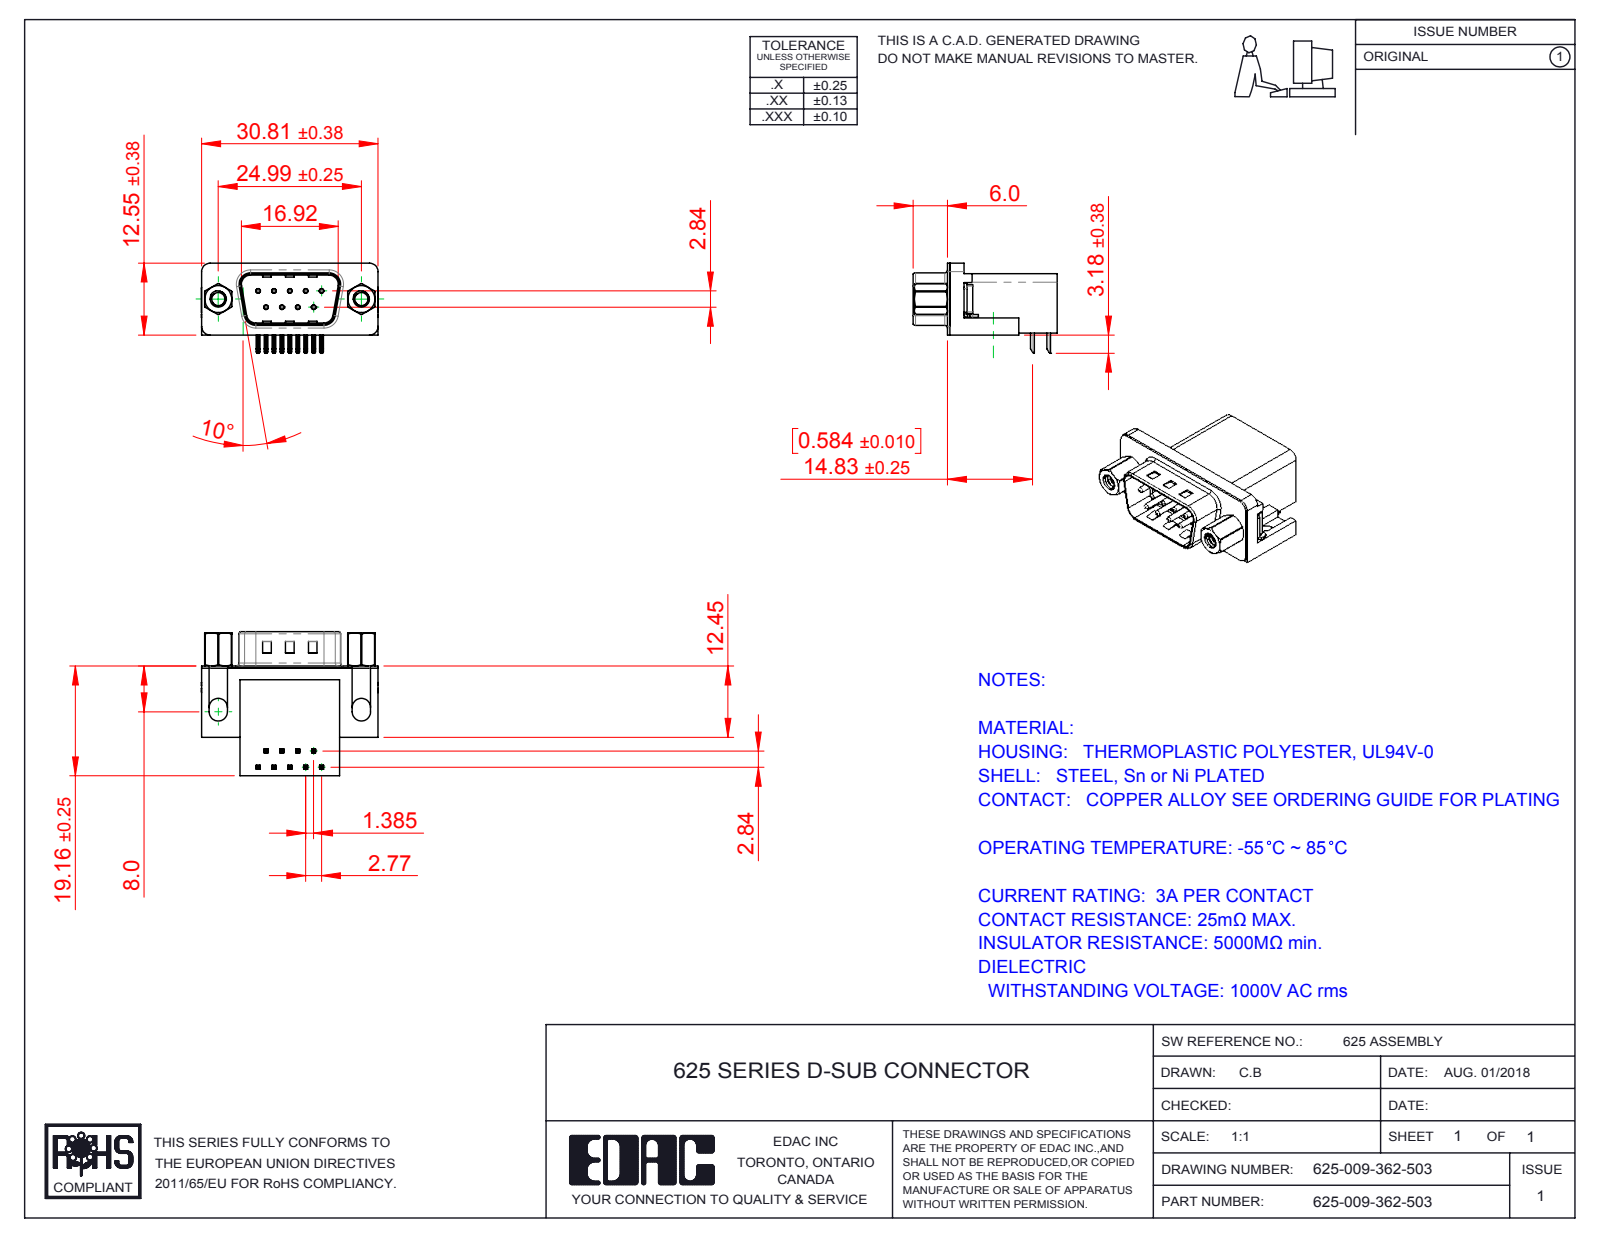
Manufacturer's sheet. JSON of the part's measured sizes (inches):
{"part_name": "625 4-40 Hex Standoff 5; 625 Non Board Mount; 625 Contact Bottom; 625-009-362-503 (+4 more)", "step_written_by": "SolidWorks 2016 (CONFIG_CONTROL_DESIGN)", "units": "inches", "bodies": {"solids": 17, "faces": 1117, "planar": 597, "cylindrical": 385, "other": 135}, "overall_size": [1.216, 0.991, 0.619], "volume_in3": 0.284, "surface_area_in2": 8.215, "round_holes": [[0.014, 9], [0.031, 9], [0.089, 2], [0.09, 2], [0.157, 2], [0.189, 2], [0.197, 2]], "round_bosses_or_shafts": [[0.03, 9], [0.193, 2], [0.187, 2], [0.154, 2], [0.11, 2]], "partial_cylinders_radius": [[0.01, 44], [0.005, 18], [0.039, 16], [0.02, 9], [0.059, 8], [0.063, 8], [0.035, 4], [0.079, 4]], "face_to_face_distances": [0.016, 0.407, 0.739, 0.754, 0.64, 0.098, 0.114, 0.014, 0.421, 0.264], "hole_center_spacings": [0.124, 0.109, 0.218, 0.198, 0.198, 0.327, 0.294, 0.295]}
